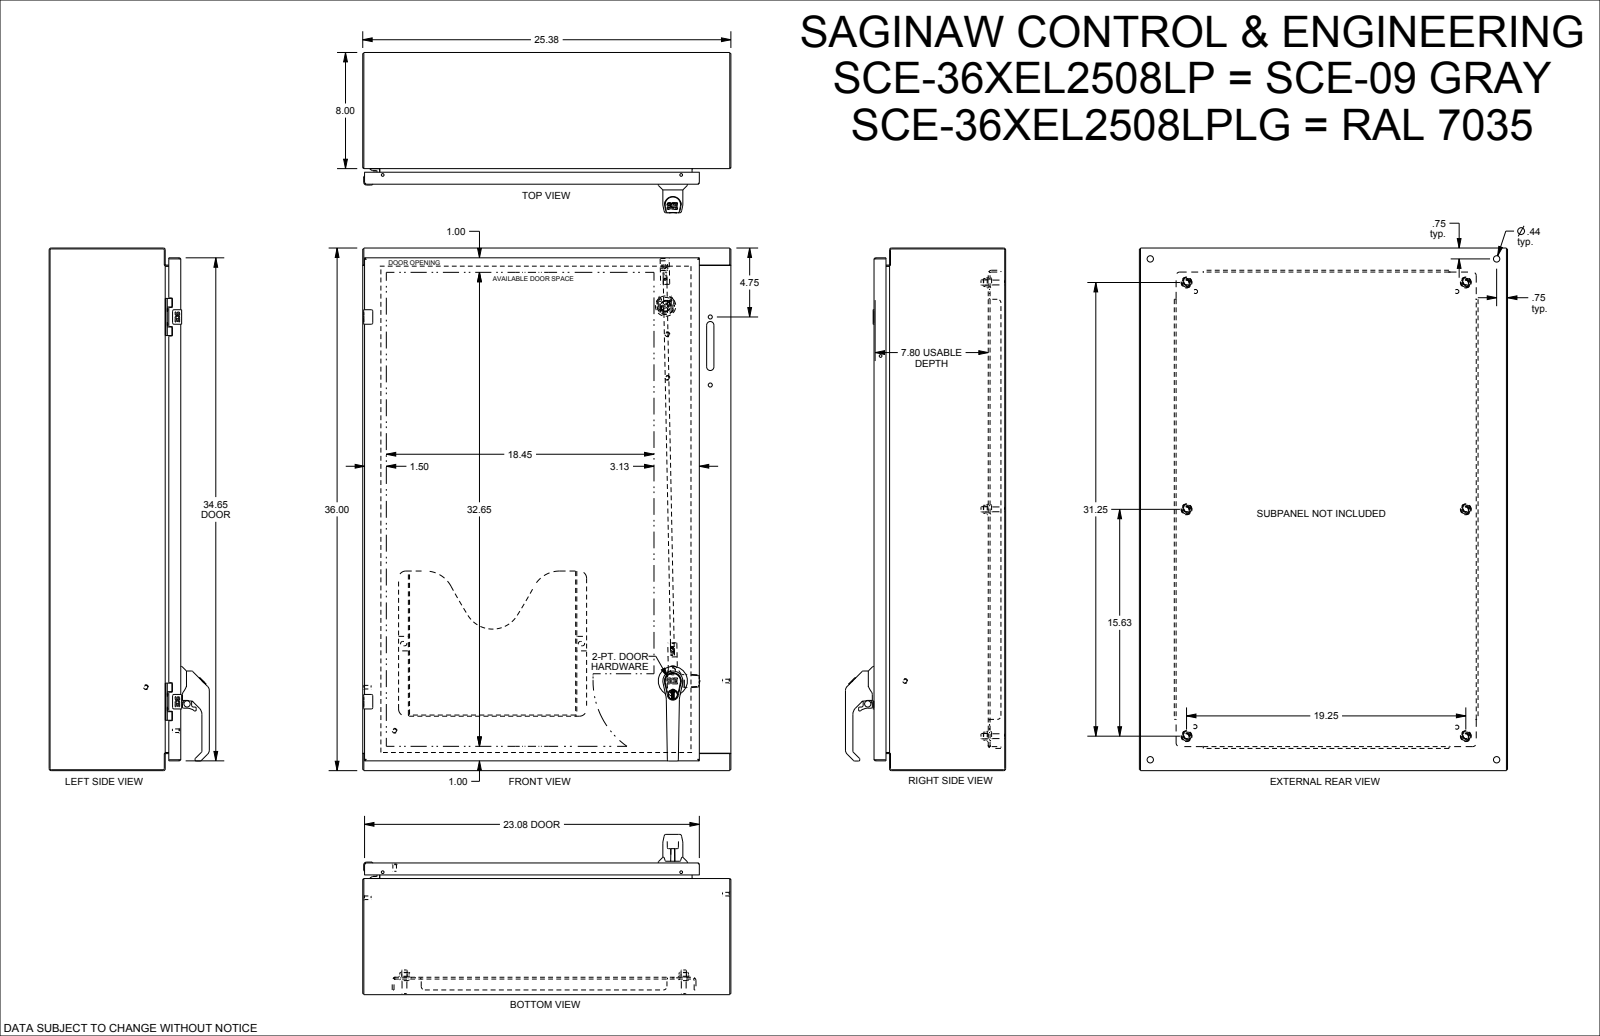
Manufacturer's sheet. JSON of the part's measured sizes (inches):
{"part_name": "SCE-30XEL2508LPLG", "step_written_by": "SolidWorks 2019 (CONFIG_CONTROL_DESIGN)", "units": "inches", "bodies": {"solids": 0, "faces": 4640, "planar": 1749, "cylindrical": 1224, "other": 1667}, "overall_size": [30, 25.375, 11.041], "round_holes": [[0.281, 6], [0.266, 5], [0.172, 4], [0.205, 4], [0.244, 4], [0.367, 4], [0.375, 4], [0.437, 4], [0.5, 4], [0.25, 3], [0.04, 2], [0.138, 2]], "round_bosses_or_shafts": [[0.248, 8], [0.17, 6], [0.25, 5], [0.366, 4], [0.332, 4], [0.24, 4], [0.563, 3], [0.196, 3]], "partial_cylinders_radius": [[0.03, 71], [0.015, 54], [0.02, 43], [0.02, 36], [0.01, 32], [0.039, 30], [0.005, 26], [0.04, 25]], "face_to_face_distances": [0.075, 0.075, 8.998, 8.923, 9.073, 8.998, 1.2, 7.873, 0.125, 7.923], "hole_center_spacings": [20.5, 0.985, 0.02, 0.493, 0.494, 4.493, 0.472, 0.725]}
